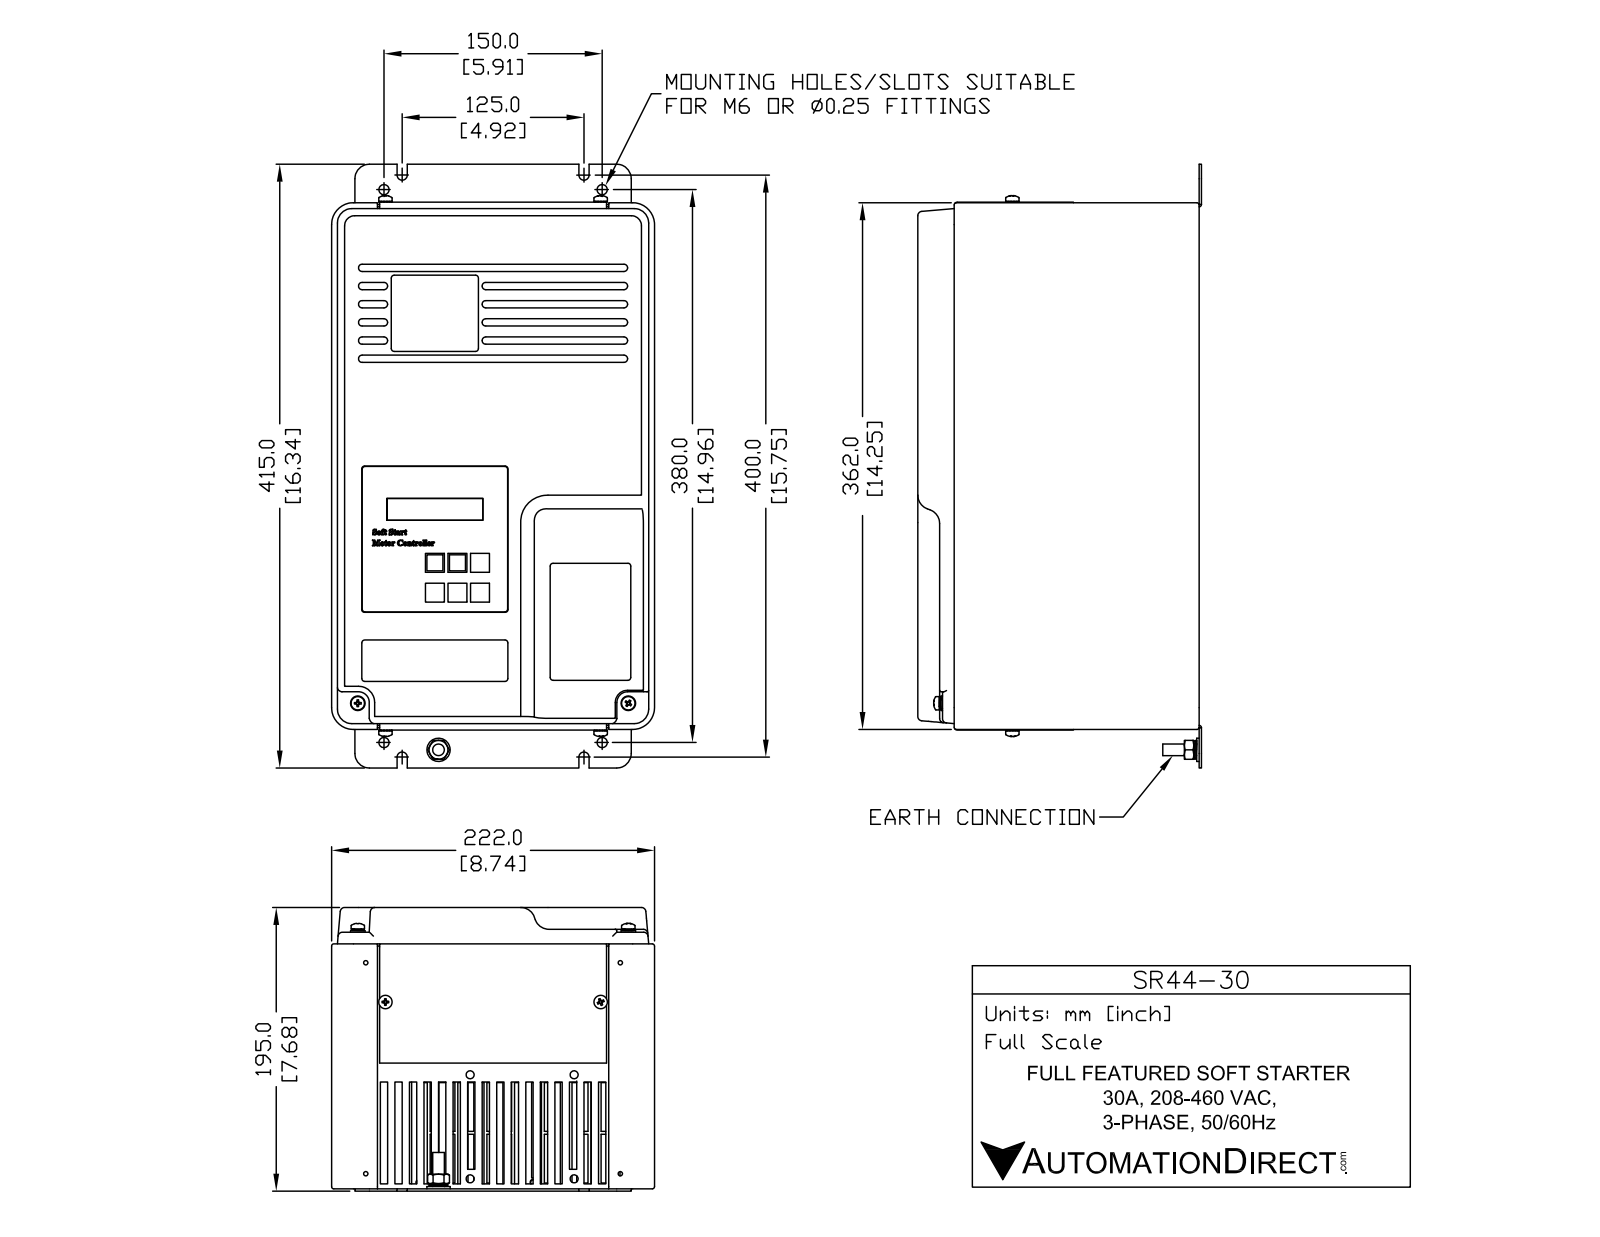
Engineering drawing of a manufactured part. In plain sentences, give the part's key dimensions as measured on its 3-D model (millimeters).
The part is named "SR44-30". Its 3-D file was written by "SolidWorks 2013 (AUTOMOTIVE_DESIGN)". It is 1 solid with 768 faces: 455 planar, 175 cylindrical and 138 other. Overall it measures 415 by 222 by 194.7 millimeters. Its volume is 8 231 000 cubic millimeters and its surface area 711 054 square millimeters. Round holes: 4 of diameter 7. Round bosses or shafts: 4 of diameter 10, 1 of diameter 16, 1 of diameter 8. Partial cylindrical surfaces (rounded edges, fillets, slot ends): 30 of radius 2.5, 28 of radius 2.4, 12 of radius 2.49, 11 of radius 1.5, 8 of radius 3, 8 of radius 10, 6 of radius 2, 4 of radius 3.5. The main face-to-face distances are 10.19, 20.38, 30.57, 40.76, 50.95, 61.14, 71.33, 5.9, 81.52, 216.1. The hole center spacings are 150, 380, 408.53.
